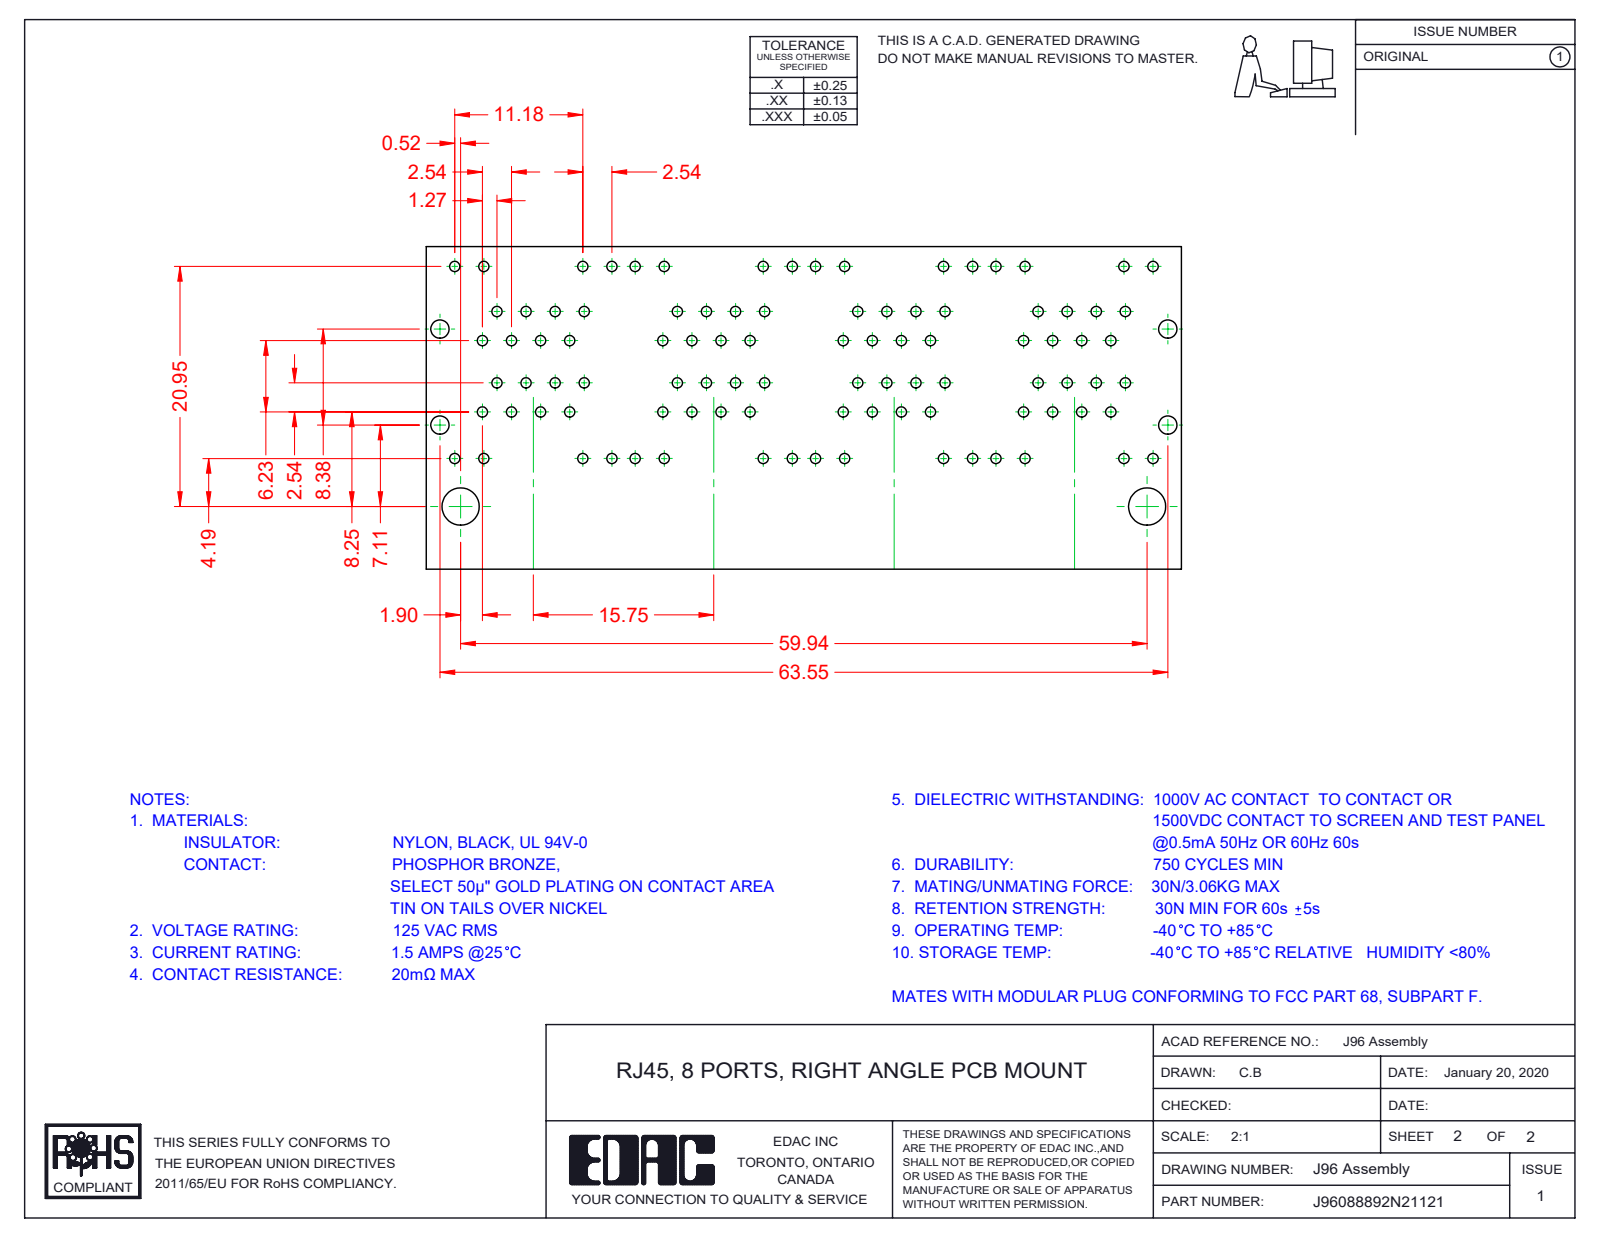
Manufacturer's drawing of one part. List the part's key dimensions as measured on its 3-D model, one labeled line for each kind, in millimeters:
Part name (STEP PRODUCT): 96 LED LH Upper_2-Red; 96 LED LH Lower_2-Red; 96 Back Plate_8 Ports; 96 Insulator Insert (+8 more)
STEP written by: SolidWorks 2016 (CONFIG_CONTROL_DESIGN)
Units: millimetres
Bodies: 96 solids, 7642 faces (6069 planar, 1307 cylindrical, 266 other)
Overall size (bounding box): 64.05 × 29.58 × 28.68
Volume: 24 160 mm³ · Surface area: 63 658 mm²
Round holes (diameter × count): ⌀1.7 ×3
Round bosses / shafts (diameter × count): ⌀1.68 ×3
Partial cylindrical surfaces — rounded edges, fillets, slot ends (radius × count): R0.25 ×124, R0.35 ×73, R1 ×72, R0.5 ×49, R0.91 ×32, R0.2 ×21, R0.7 ×11, R0.22 ×8
Main face-to-face distances: 15.75, 0.35, 9.95, 1.17, 1.6, 0.54, 9.98, 10.18, 12.67, 3.37
Hole centre spacings: 15.75, 31.5
